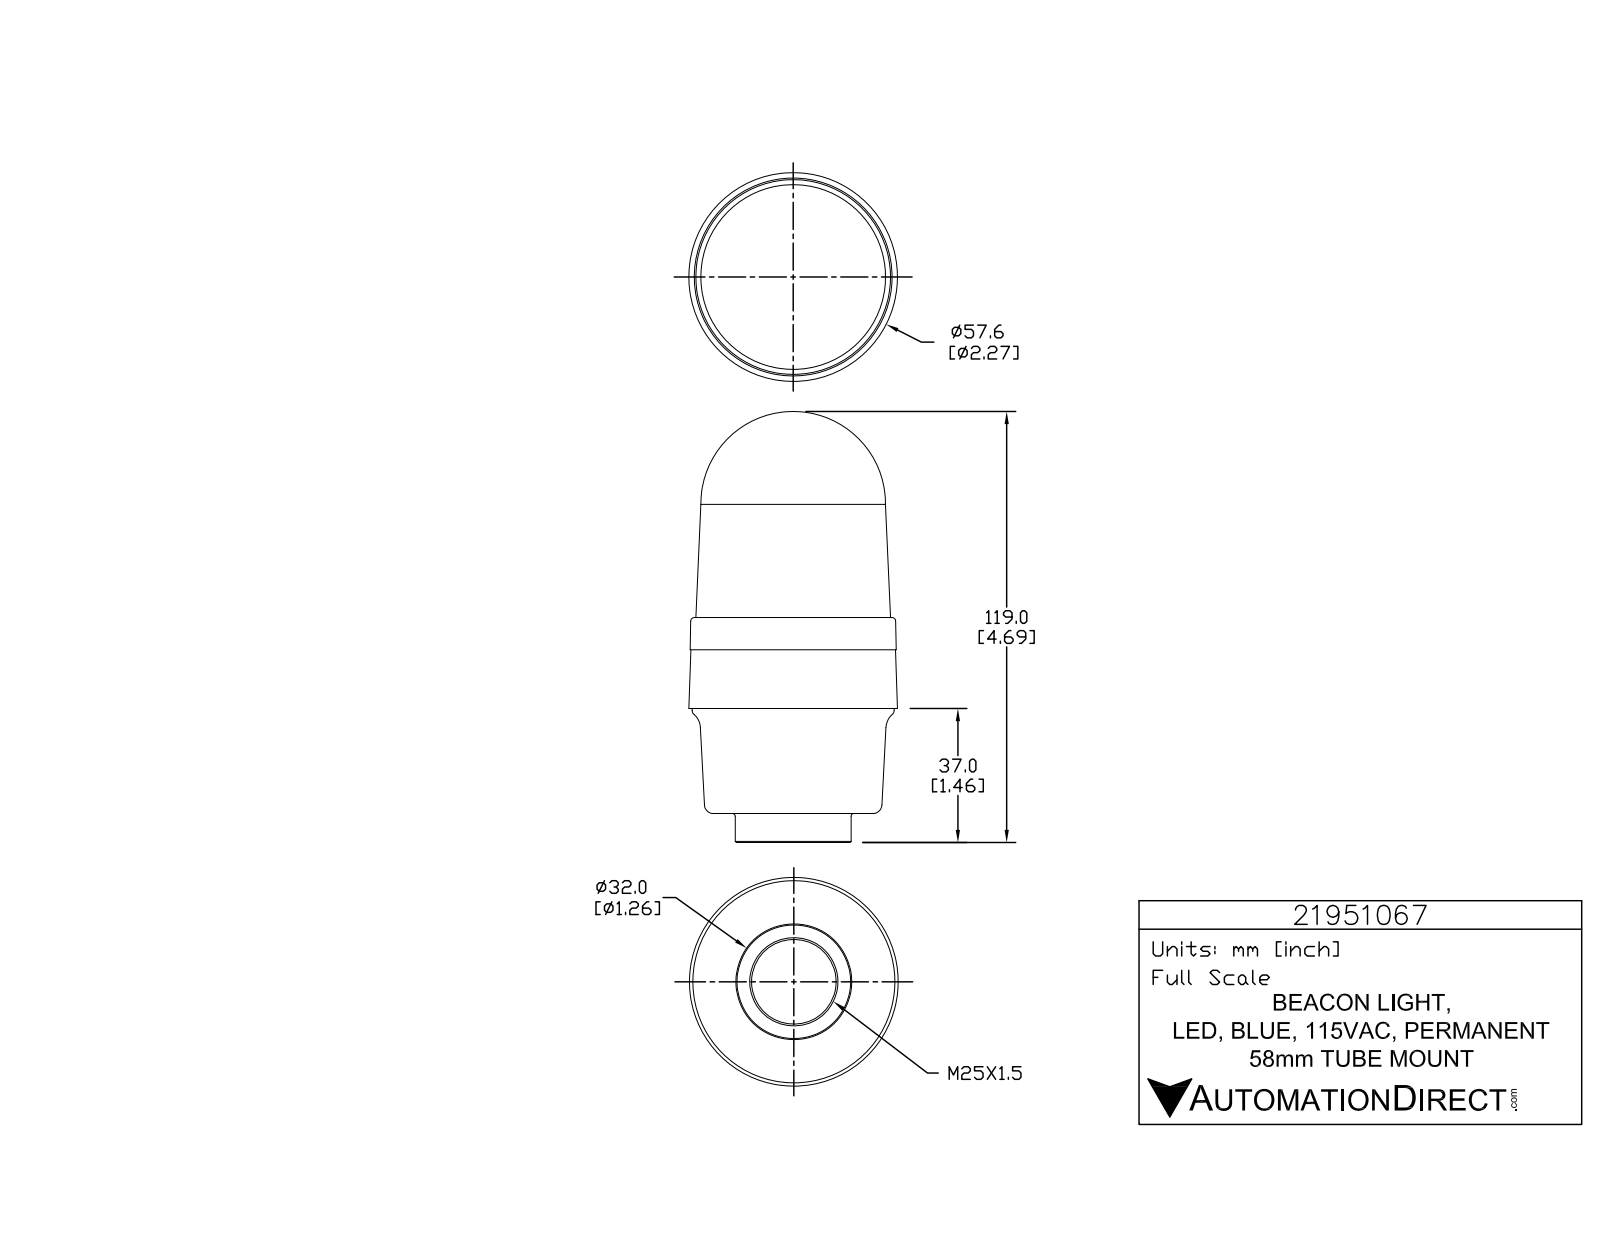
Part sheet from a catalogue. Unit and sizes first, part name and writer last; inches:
Units: inches
Overall size (bounding box): 4.685 × 2.269 × 2.269
Round holes (diameter × count): ⌀0.039 ×3, ⌀0.92 ×1
Round bosses / shafts (diameter × count): ⌀0.226 ×3, ⌀0.056 ×3, ⌀2.197 ×1, ⌀1.26 ×1
Partial cylindrical surfaces — rounded edges, fillets, slot ends (radius × count): R0.008 ×6, R0.008 ×6, R0.008 ×6, R0.131 ×6, R0.004 ×3, R0.005 ×3, R0.008 ×3, R0.008 ×3
Main face-to-face distances: 0.315, 1.142, 1.457, 0.988, 2.13, 2.445, 0.35, 0.638, 1.78, 2.094
Volume: 13.89 in³ · Surface area: 34.06 in²
Bodies: 1 solid, 791 faces (525 planar, 168 cylindrical, 98 other)
Part name (STEP PRODUCT): 21951067
STEP written by: SolidWorks 2015 (AUTOMOTIVE_DESIGN)
